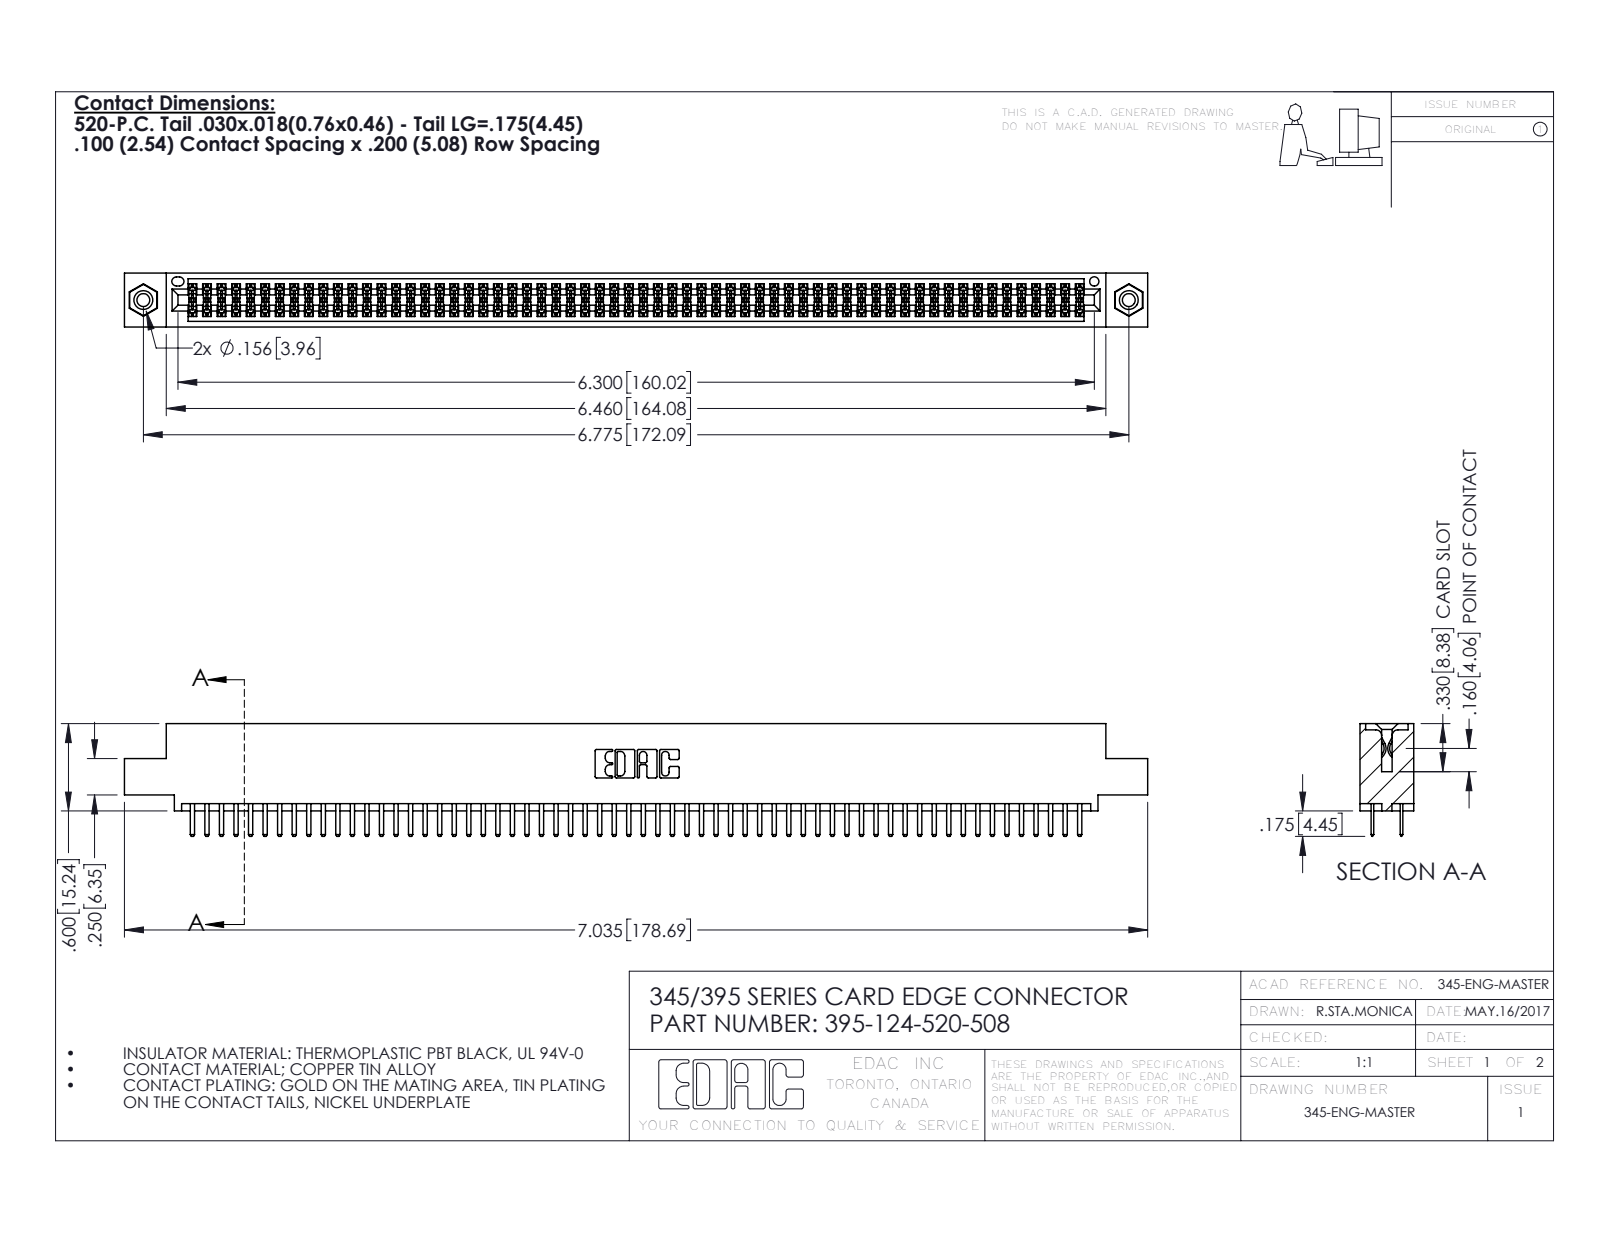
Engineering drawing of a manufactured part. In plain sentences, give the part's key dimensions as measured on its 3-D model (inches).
The part is named "395-124-520-508; 345-250-001_345-250-003-102; 345 Part_0.110 Offset - 0.156 Dia-TI; 345-292-001_345-293-120". Its 3-D file was written by "SolidWorks 2016 (CONFIG_CONTROL_DESIGN)". It is 127 solids with 6886 faces: 4456 planar, 2414 cylindrical and 16 other. Overall it measures 7.035 by 0.775 by 0.37 inches. Its volume is 1.062 cubic inches and its surface area 40.47 square inches. Round holes: 2 of diameter 0.089, 2 of diameter 0.125, 2 of diameter 0.156, 1 of diameter 0.064. Round bosses or shafts: 2 of diameter 0.155. Partial cylindrical surfaces (rounded edges, fillets, slot ends): 186 of radius 0.006, 128 of radius 0.01, 22 of radius 0.01, 6 of radius 0.007, 6 of radius 0.031, 3 of radius 0.026, 2 of radius 0.014, 2 of radius 0.019. The main face-to-face distances are 0.072, 0.298, 0.2, 0.37, 0.098, 0.272, 0.025, 0.225, 0.022, 0.072. The hole center spacings are 0.27, 6.539, 6.775.
